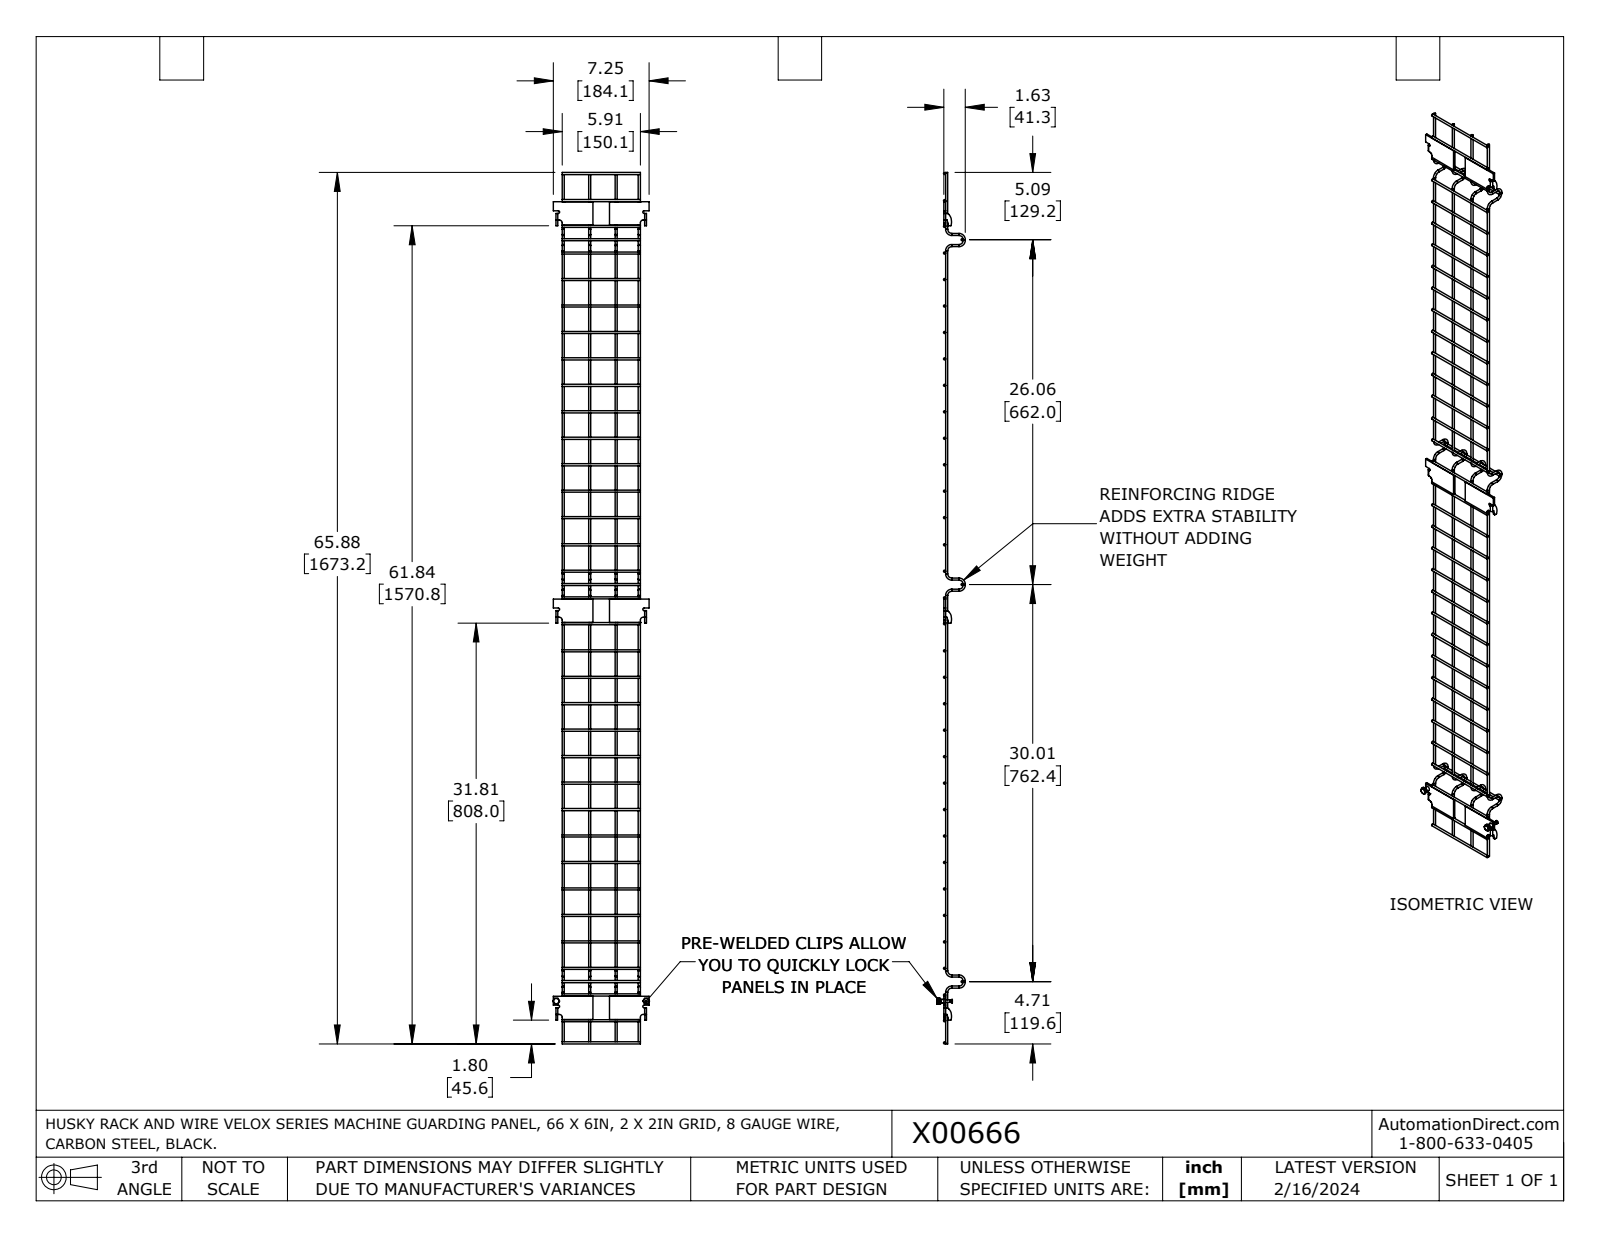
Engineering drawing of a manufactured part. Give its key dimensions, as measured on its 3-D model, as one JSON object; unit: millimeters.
{"part_name": "X00666", "step_written_by": "SolidWorks 2023 (AUTOMOTIVE_DESIGN)", "units": "millimeters", "bodies": {"solids": 51, "faces": 399, "planar": 190, "cylindrical": 137, "other": 72}, "overall_size": [1673.2, 185.8, 53.4], "volume_mm3": 234800, "surface_area_mm2": 212700, "round_holes": [[5.1, 2], [6.4, 2]], "round_bosses_or_shafts": [[4.1, 69], [9.9, 2], [6.2, 2], [4.7, 2]], "partial_cylinders_radius": [[2.5, 6], [5.5, 6], [6.4, 3], [22, 3], [0.2, 2], [1.7, 2], [3.4, 2]], "face_to_face_distances": [3.4, 3.2, 44.8, 762.8, 11.9, 162, 762.4, 1525.2, 71.1, 102.8], "hole_center_spacings": [172.9]}
